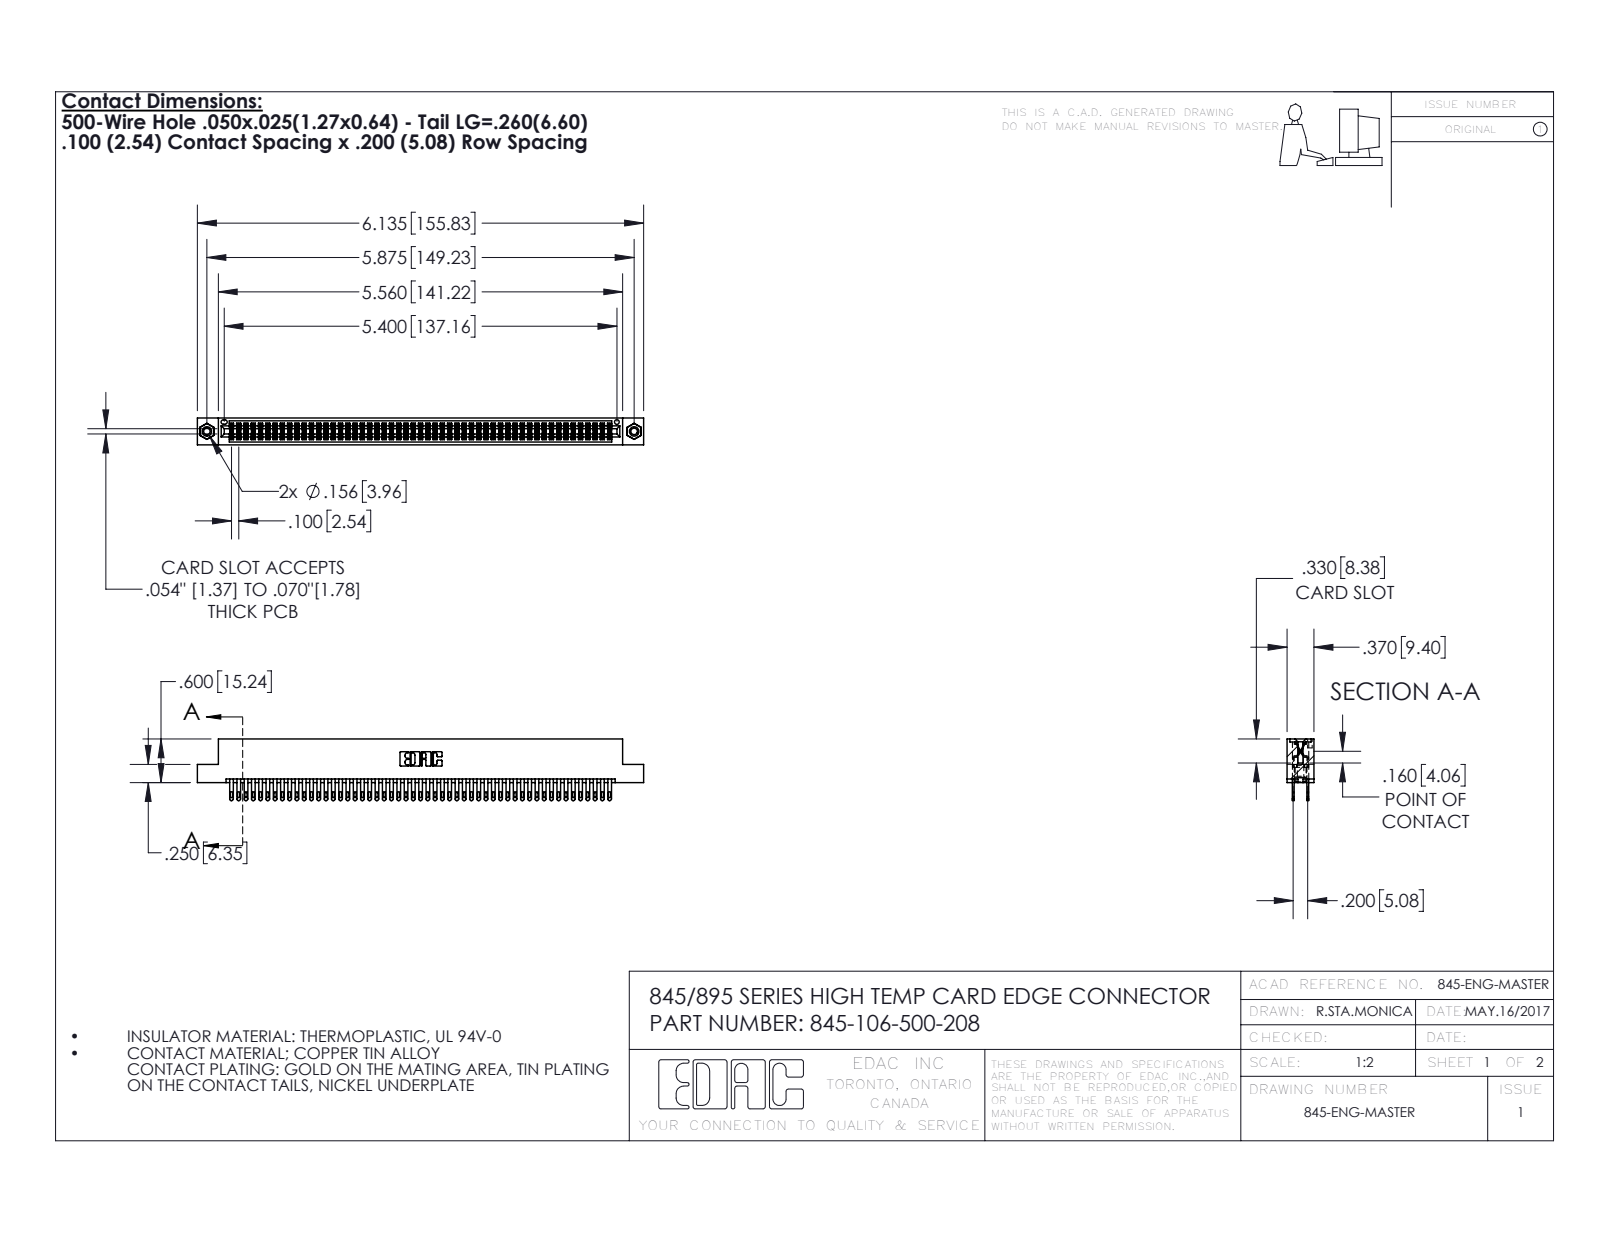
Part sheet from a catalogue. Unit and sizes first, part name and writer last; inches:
Units: inches
Overall size (bounding box): 6.135 × 0.847 × 0.37
Round holes (diameter × count): ⌀0.089 ×2, ⌀0.125 ×2, ⌀0.156 ×2, ⌀0.064 ×1
Round bosses / shafts (diameter × count): ⌀0.155 ×2
Partial cylindrical surfaces — rounded edges, fillets, slot ends (radius × count): R0.006 ×159, R0.016 ×106, R0.02 ×106, R0.01 ×22, R0.007 ×6, R0.031 ×6, R0.026 ×3, R0.014 ×2
Main face-to-face distances: 0.072, 0.298, 0.2, 0.098, 0.272, 0.025, 0.37, 0.225, 0.175, 0.149
Hole centre spacings: 0.27, 5.639, 5.875
Volume: 0.949 in³ · Surface area: 37.67 in²
Bodies: 109 solids, 5062 faces (2974 planar, 2072 cylindrical, 16 other)
Part name (STEP PRODUCT): 345 Part_Flush Mounting Lugs - 0.156 Dia-TI; 345-292-001_345-293-100; 345-250-001_345-250-003-102; 345-106-500-208
STEP written by: SolidWorks 2016 (CONFIG_CONTROL_DESIGN)
